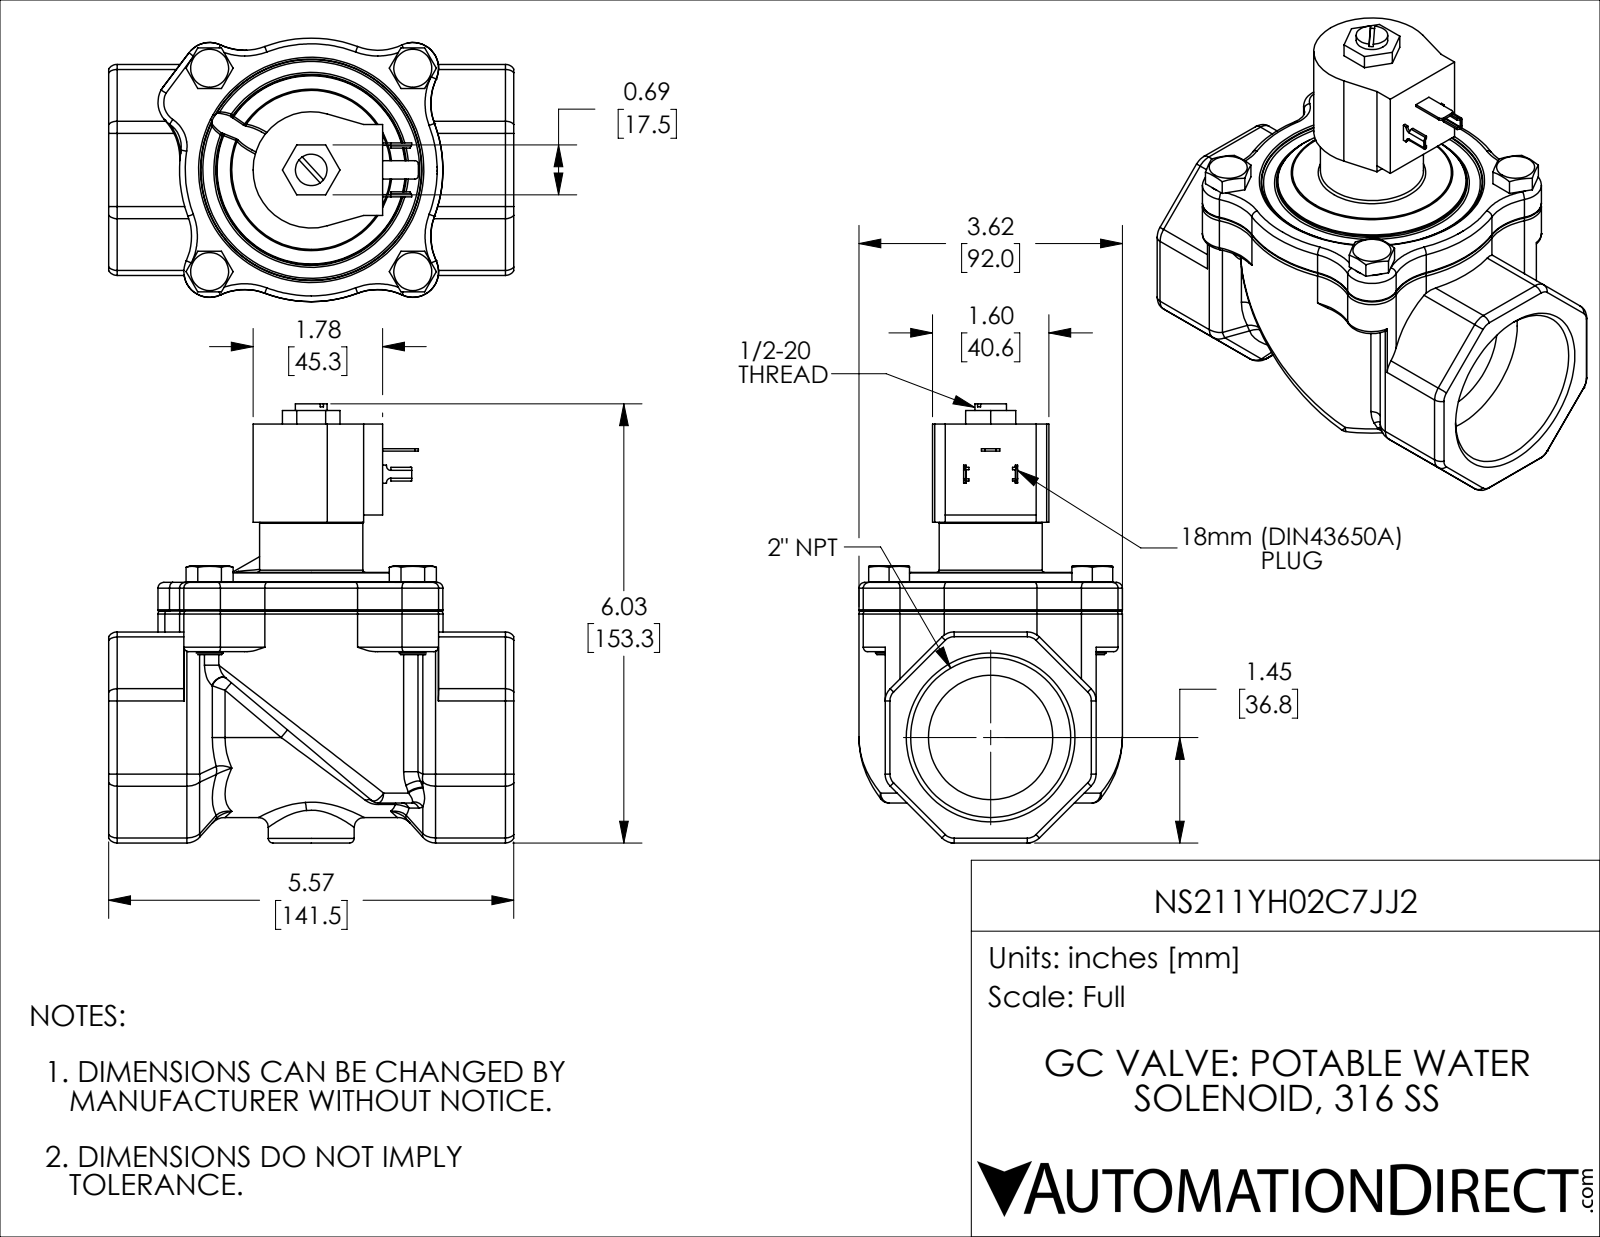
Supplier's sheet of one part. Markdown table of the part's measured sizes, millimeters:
| quantity | value |
| --- | --- |
| part name | NS211YH02C7JJ2 |
| STEP written by | SolidWorks 2024 (CONFIG_CONTROL_DESIGN) |
| units | millimeters |
| bodies | 9 solids, 606 faces (166 planar, 205 cylindrical, 235 other) |
| overall size | 153.3 × 141.5 × 92 |
| volume | 611 200 mm³ |
| surface area | 110 800 mm² |
| round holes (diameter × count) | 7.9 × 4, 11 × 4, 3 × 1, 3.2 × 1, 6 × 1, 11 × 1, 12.8 × 1, 21.5 × 1, 24.1 × 1, 43.4 × 1, 55.9 × 1, 73 × 1 |
| round bosses / shafts (diameter × count) | 12.8 × 4, 9.4 × 4, 76.8 × 1, 36 × 1, 30 × 1 |
| partial cylindrical surfaces (radius × count) | 3.5 × 29, 6 × 28, 20 × 15, 9 × 8, 0.2 × 4, 1 × 4, 1.3 × 2, 1.5 × 2 |
| main face-to-face distances | 3, 56.1, 85.4, 73.7, 73.7, 13, 10, 34.3, 34, 31 |
| hole center spacings | 50.2, 50.2, 71, 71, 50.2, 59.7, 71, 71 |
